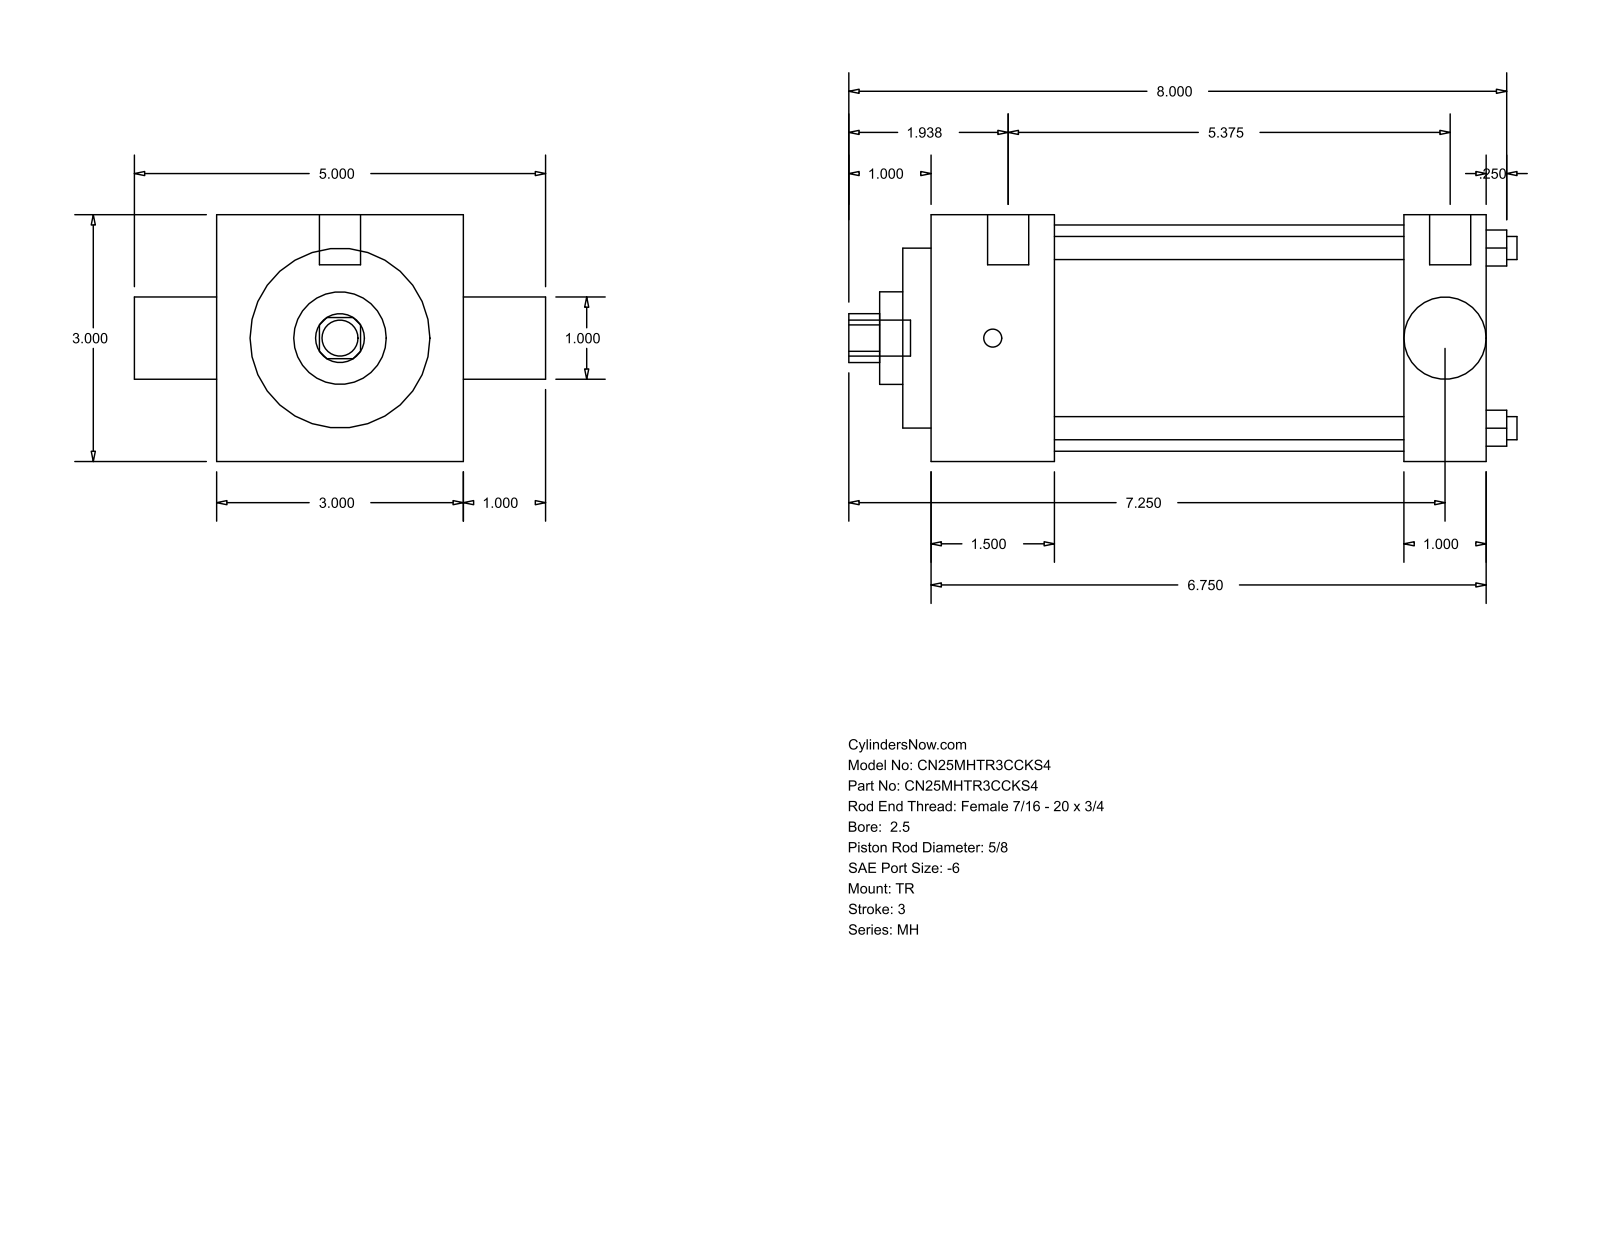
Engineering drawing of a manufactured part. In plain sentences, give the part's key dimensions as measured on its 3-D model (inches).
The part is named "MH_TR__0250_0.625". Its 3-D file was written by "GSSL Pune (CONFIG_CONTROL_DESIGN)". It is 0 solids with 86 faces: 61 planar, 25 cylindrical and 0 other. Overall it measures 8.125 by 5 by 3 inches. Round holes: 4 of diameter 0.281, 1 of diameter 0.625, 1 of diameter 0.998, 1 of diameter 1.125, 1 of diameter 2.187, 1 of diameter 2.75. Round bosses or shafts: 3 of diameter 0.219, 2 of diameter 0.5, 1 of diameter 0.437. Partial cylindrical surfaces (rounded edges, fillets, slot ends): 1 of radius 0.297. The main face-to-face distances are 3, 6.75, 1, 1.5, 5.25, 5.75, 4.25, 0.344, 1.844, 6.094. The hole center spacings are 1.548, 2.19, 3.097.
